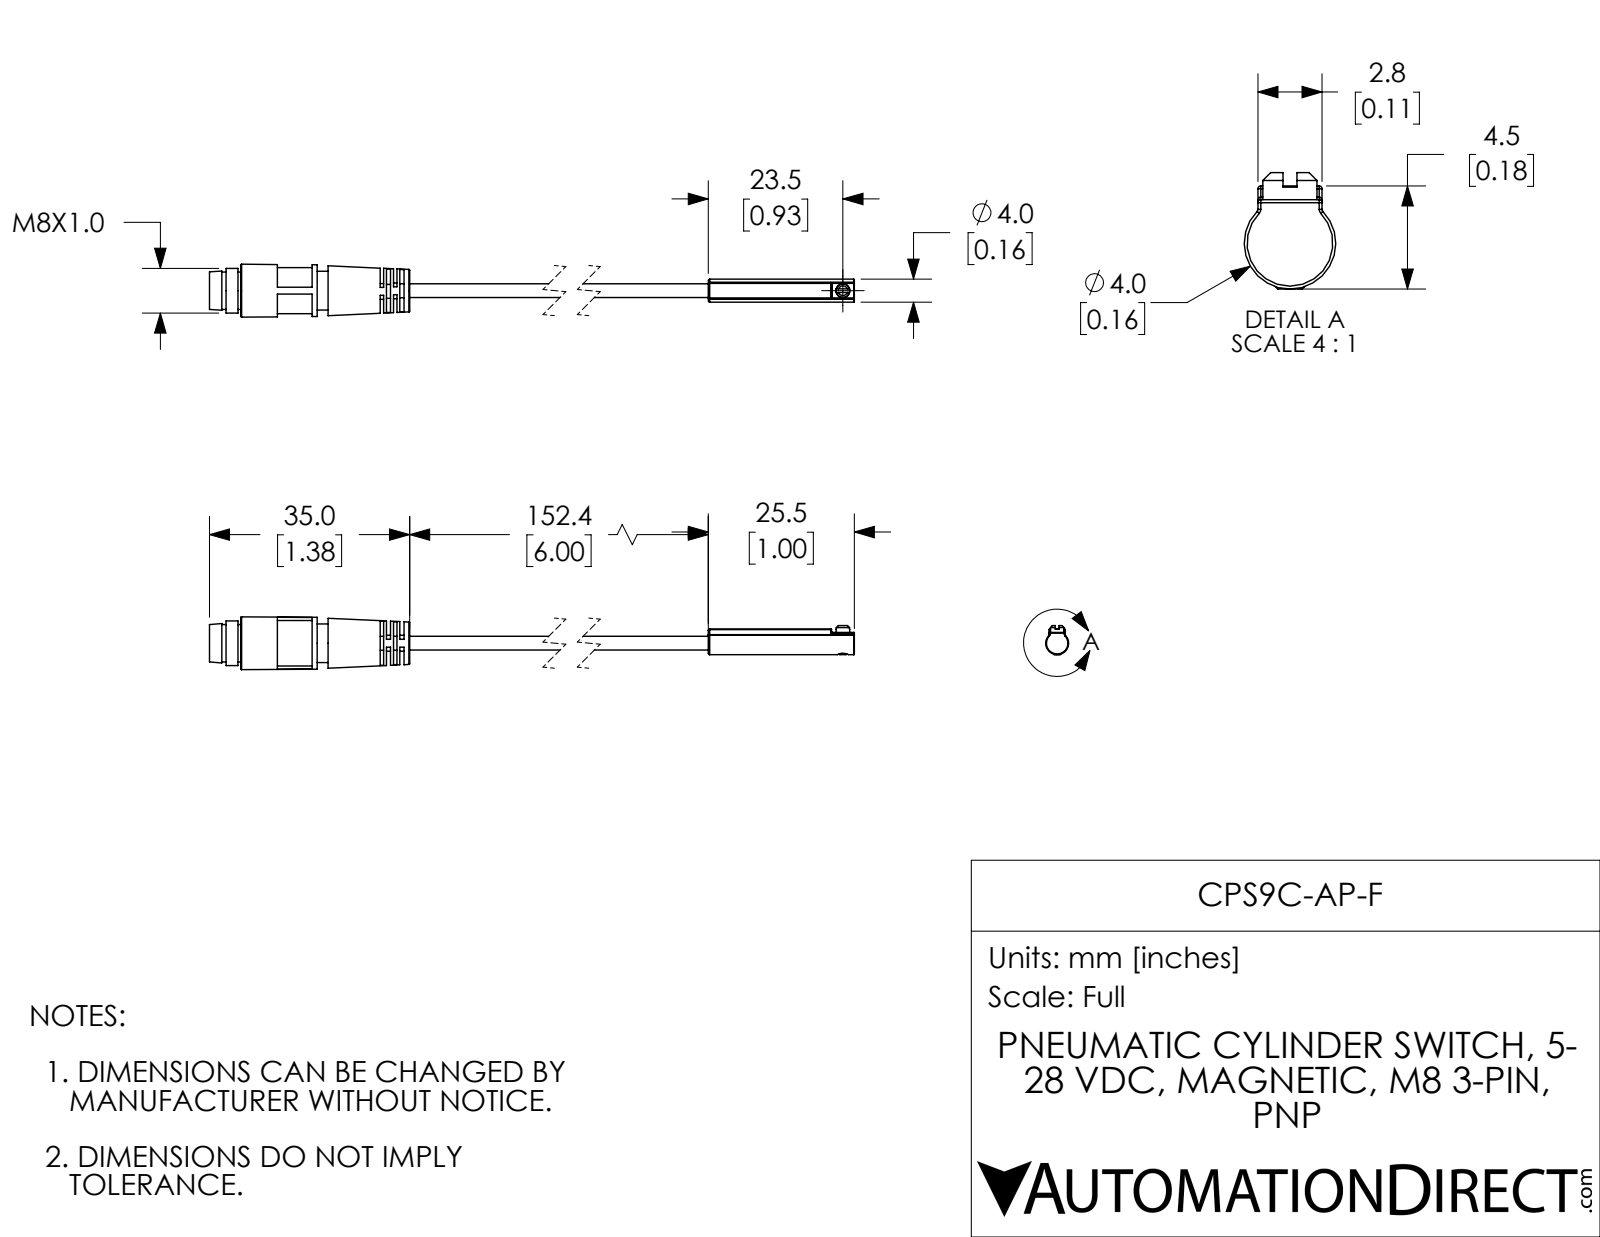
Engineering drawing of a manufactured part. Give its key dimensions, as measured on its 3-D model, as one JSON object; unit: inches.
{"part_name": "CPS9C-AP-F", "step_written_by": "SolidWorks 2019 (AUTOMOTIVE_DESIGN)", "units": "inches", "bodies": {"solids": 3, "faces": 167, "planar": 67, "cylindrical": 55, "other": 45}, "overall_size": [8.38, 0.363, 0.363], "volume_in3": 0.162, "surface_area_in2": 4.792, "round_holes": [[0.076, 1], [0.214, 1], [0.228, 1]], "round_bosses_or_shafts": [[0.039, 3], [0.316, 1], [0.307, 1], [0.266, 1], [0.257, 1], [0.094, 1], [0.093, 1]], "partial_cylinders_radius": [[0.005, 13], [0.01, 3], [0.054, 2], [0.055, 2], [0.079, 1]], "face_to_face_distances": [0.048, 0.072, 0.092, 0.024, 0.02, 0.044, 1.073, 0.981, 0.02, 1.093]}
